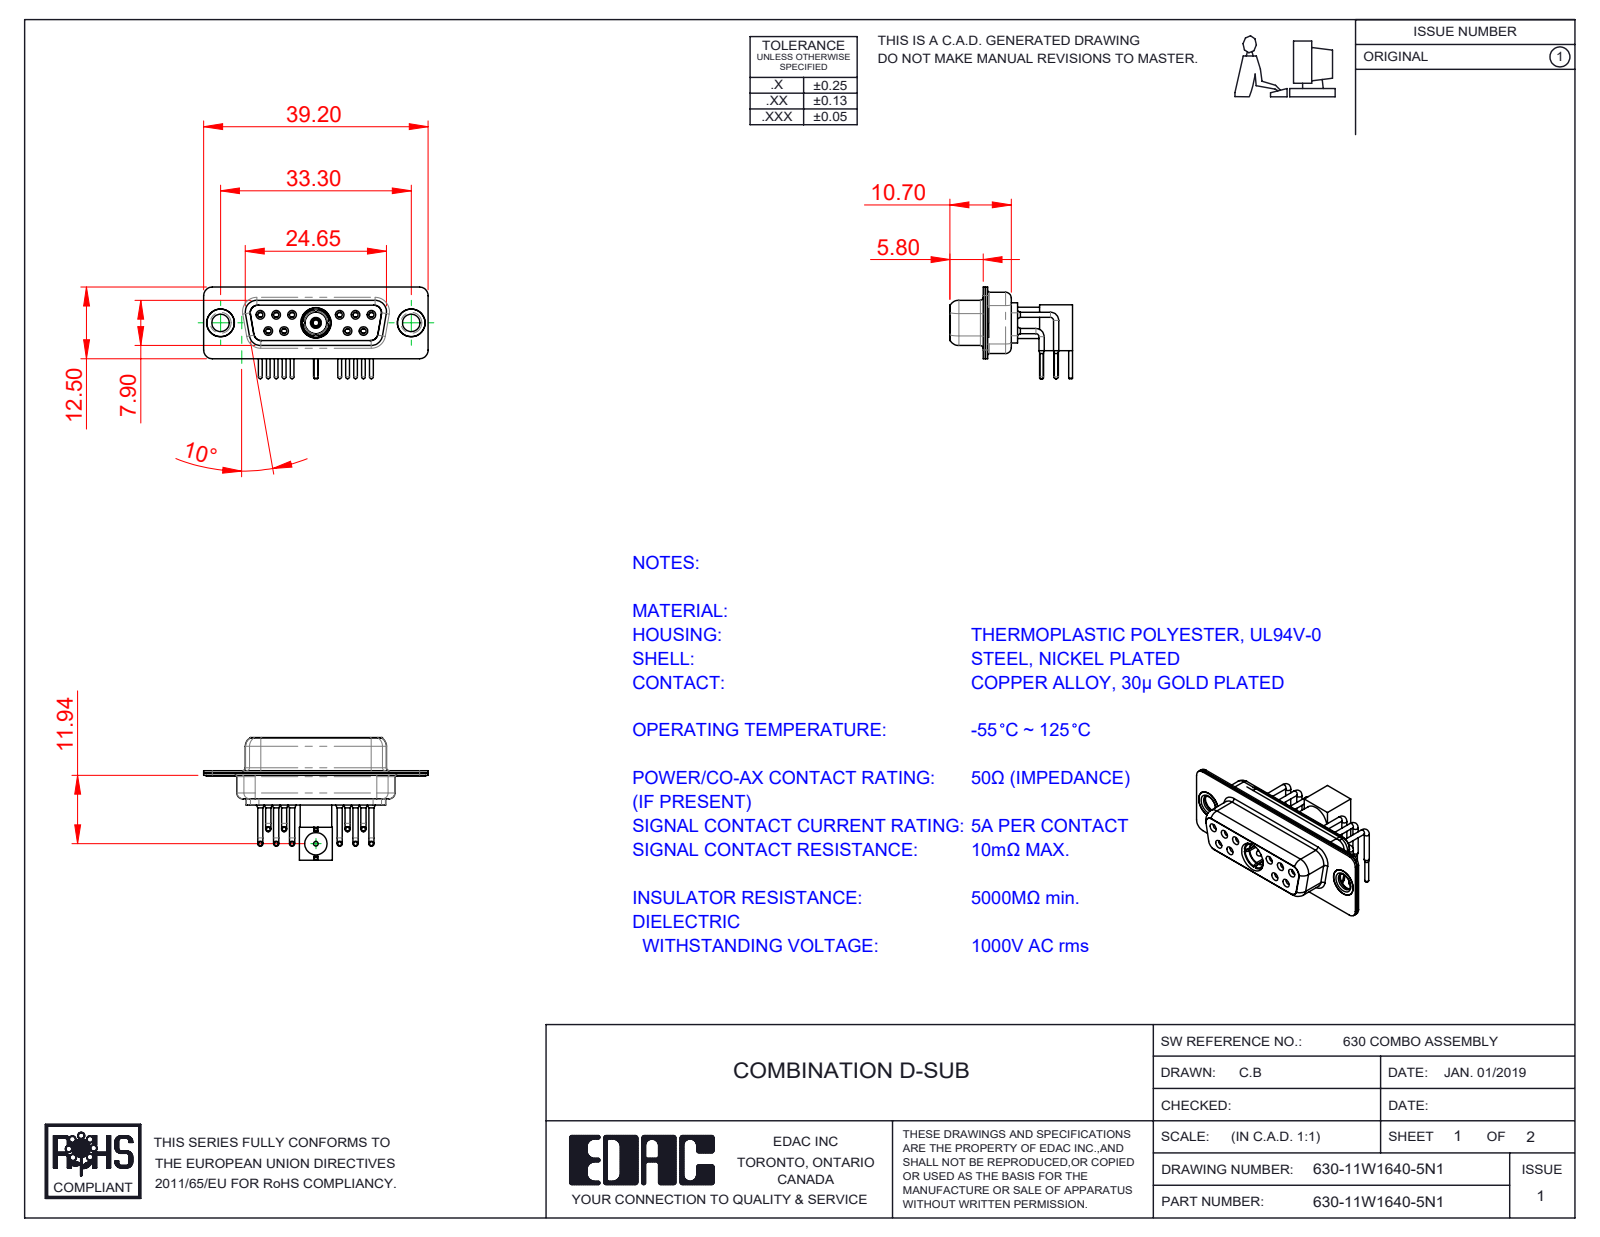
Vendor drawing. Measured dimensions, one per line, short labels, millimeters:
name: Co-Ax Plug_RA PC Tail; RA Back Shell; 630Combo Contact Row 1; 630Combo Shell Front_15 Contacts (+8 more)
written by: SolidWorks 2020 (CONFIG_CONTROL_DESIGN)
unit: mm
bodies: 21 solids, 951 faces (284 planar, 416 cylindrical, 251 other)
size: 39.2 × 21.41 × 16
volume: 2 735 mm³; area: 6 748 mm²
holes: 11× ⌀1.1, 11× ⌀1.5, 10× ⌀0.9, 10× ⌀2, 6× ⌀1.7, 4× ⌀1.6, 3× ⌀4.85, 2× ⌀3.05, 2× ⌀4, 2× ⌀4.05, 1× ⌀0.8, 1× ⌀2.83
bosses: 10× ⌀0.9, 10× ⌀0.65, 6× ⌀1.6, 3× ⌀5, 2× ⌀4.95, 2× ⌀4.8, 2× ⌀3.55, 1× ⌀5.5
rounds: 16× R1.5, 12× R1.35, 12× R2, 8× R1.6, 4× R0.25, 4× R0.5, 4× R0.6, 4× R0.65
face distances: 0.4, 1.4, 0.45, 1.8, 8.45, 8.9, 0.8, 6.2, 7.05, 1.85
hole spacings: 3.16, 2.77, 13.85, 11.08, 16.62, 5.03, 5.04, 5.54
